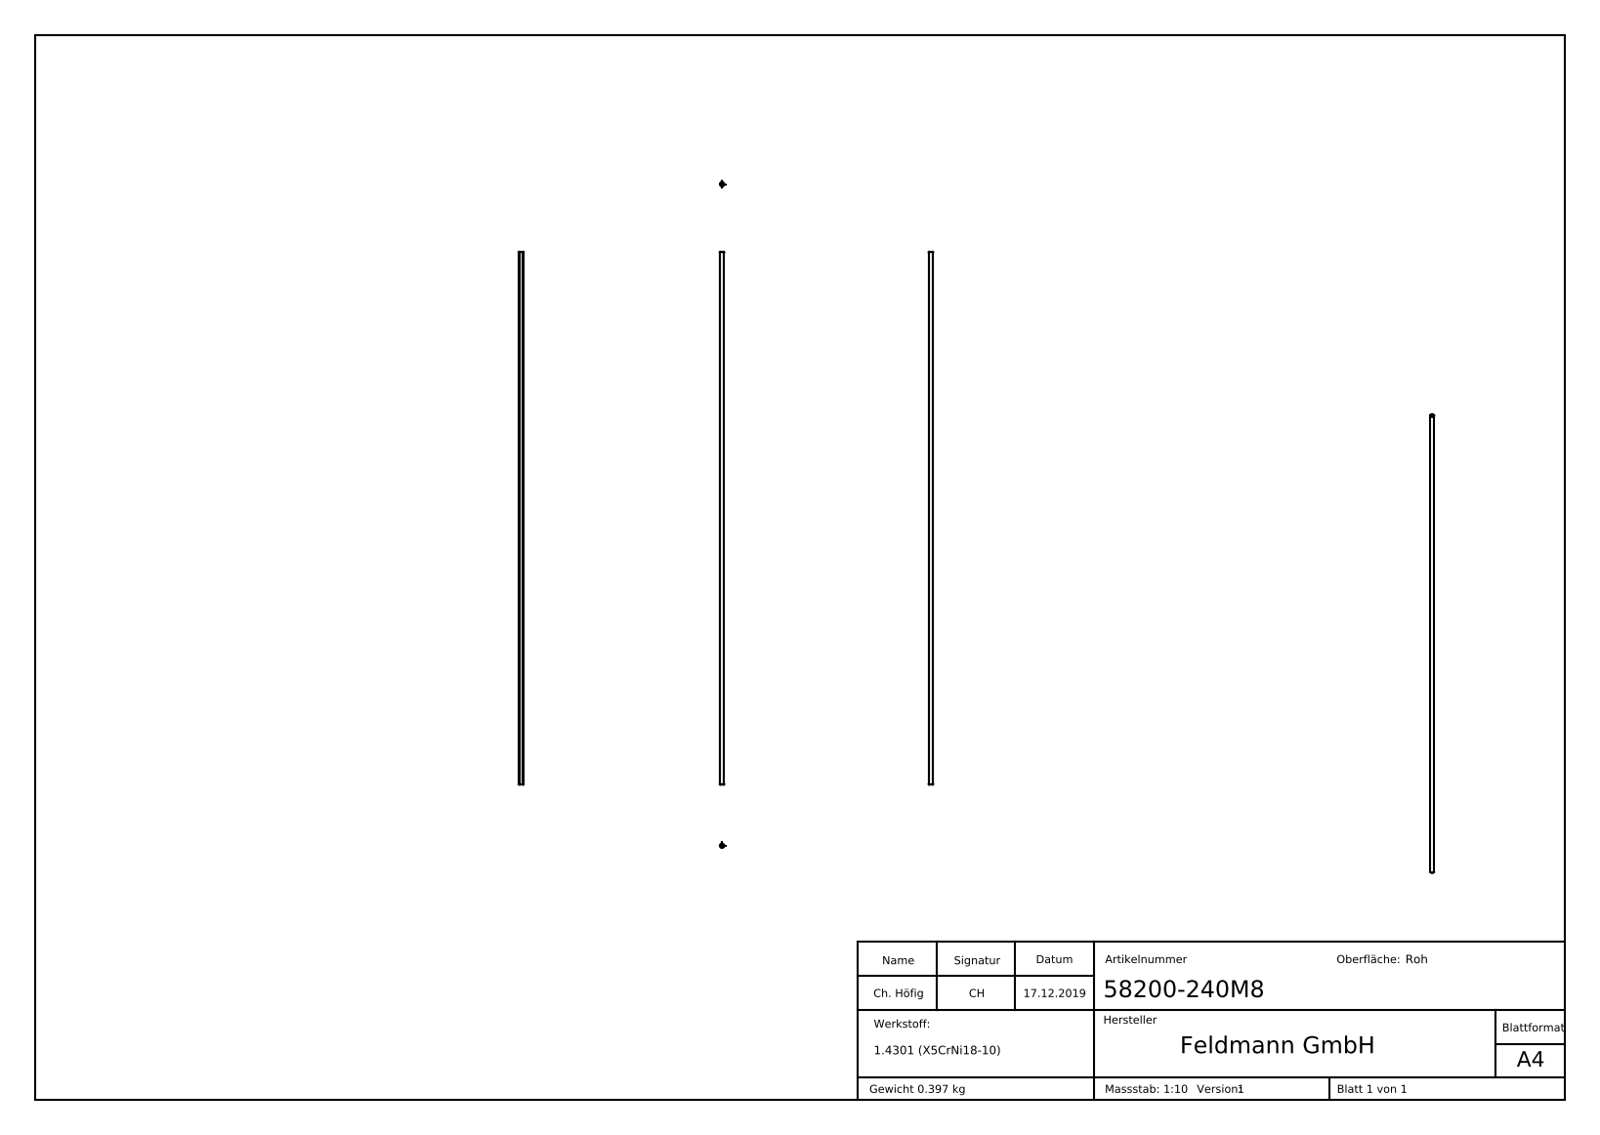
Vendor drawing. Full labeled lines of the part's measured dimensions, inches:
Part name (STEP PRODUCT): 58200-240M8
STEP written by: SolidWorks 2015 (CONFIG_CONTROL_DESIGN)
Units: inches
Bodies: 1 solid, 278 faces (146 planar, 1 cylindrical, 131 other)
Overall size (bounding box): 39.37 × 0.315 × 0.315
Volume: 3.066 in³ · Surface area: 39.06 in²
Round bosses / shafts (diameter × count): ⌀0.315 ×1
Main face-to-face distances: 39.37, 39.366, 0.014, 0.014, 0.044, 0.044, 0.058, 0.064, 0.013, 0.02
